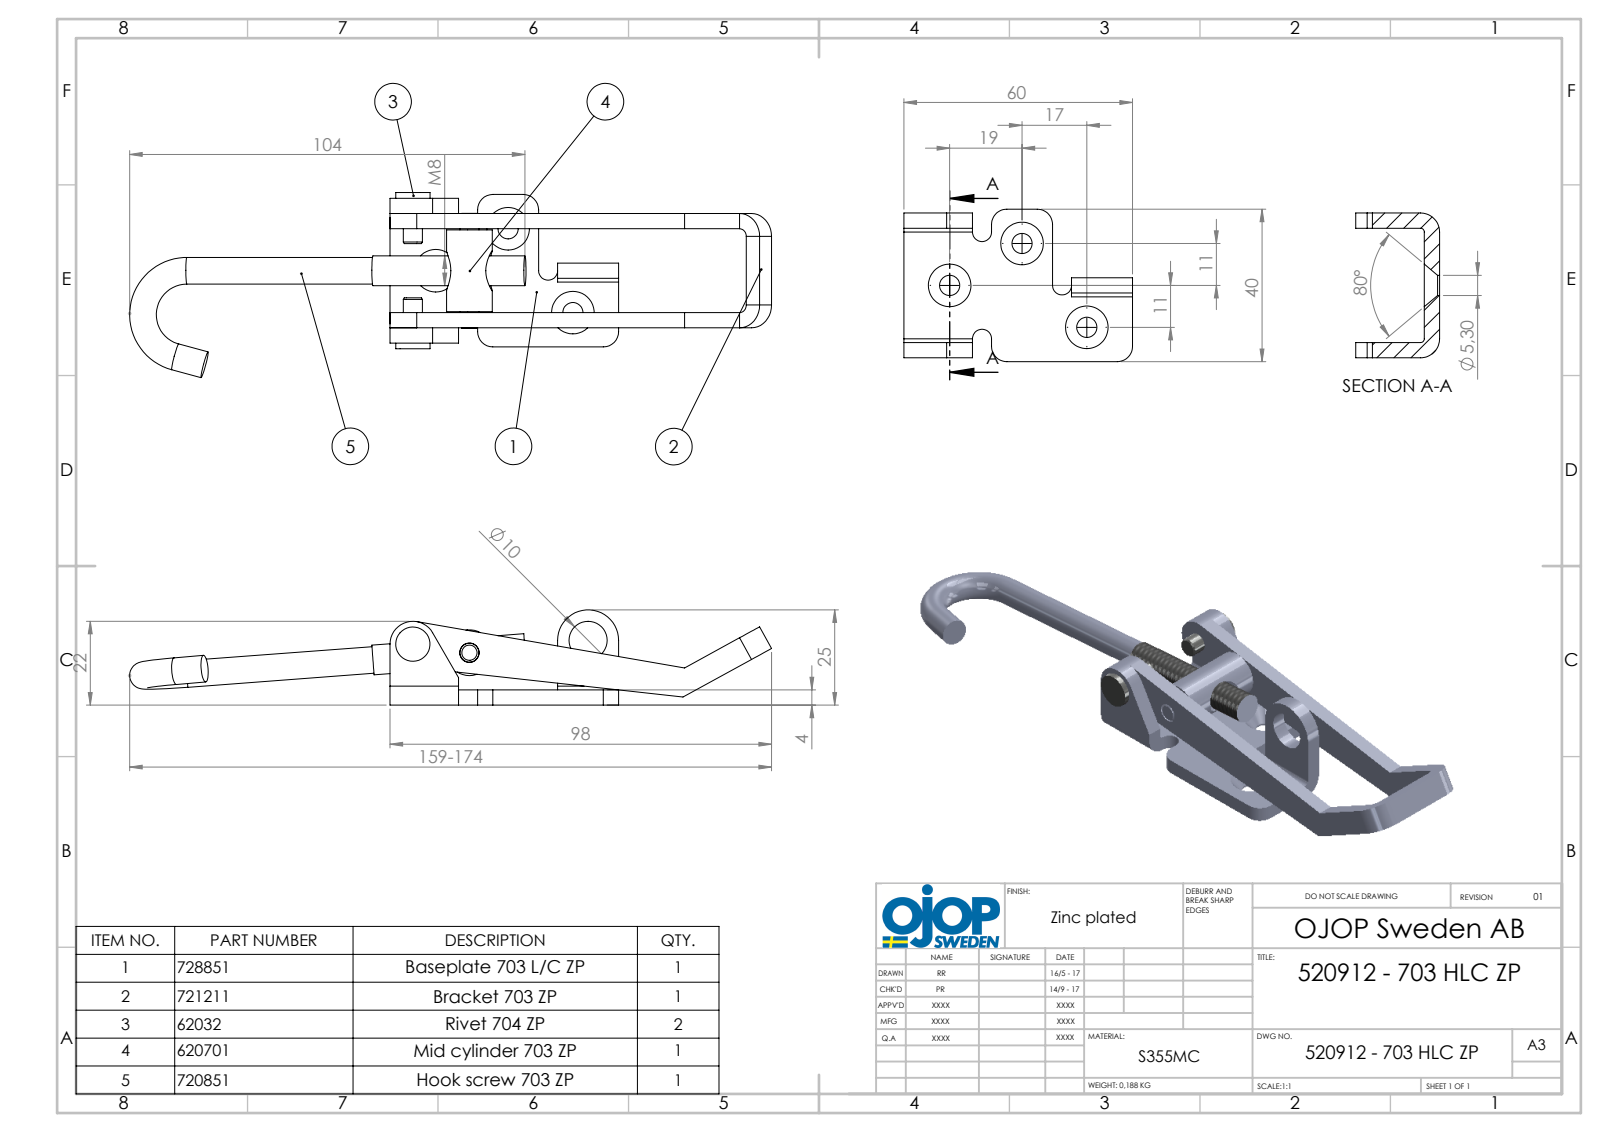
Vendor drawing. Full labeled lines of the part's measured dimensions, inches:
Part name (STEP PRODUCT): 704 - Rivet Gradin; 703 - Bygel; 520912; 703- Platta LC (+2 more)
STEP written by: SolidWorks 2015 (AUTOMOTIVE_DESIGN)
Units: inches
Bodies: 6 solids, 155 faces (65 planar, 70 cylindrical, 20 other)
Overall size (bounding box): 6.621 × 1.614 × 1.282
Volume: 1.524 in³ · Surface area: 27.07 in²
Round holes (diameter × count): ⌀0.209 ×3, ⌀0.201 ×2, ⌀0.283 ×1, ⌀0.303 ×1, ⌀0.394 ×1
Round bosses / shafts (diameter × count): ⌀0.276 ×3, ⌀0.197 ×2, ⌀0.472 ×1, ⌀0.354 ×1, ⌀0.307 ×1
Partial cylindrical surfaces — rounded edges, fillets, slot ends (radius × count): R0.157 ×4, R0.039 ×3, R0.098 ×3, R0.197 ×3, R0.236 ×3, R0.079 ×2, R0.315 ×1
Main face-to-face distances: 0.157, 1.024, 1.181, 0.866, 0.669, 0.512, 0.354, 0.827, 0.315, 1.339
Hole centre spacings: 0.591, 0.864, 1.094, 1.233, 1.482, 1.811
